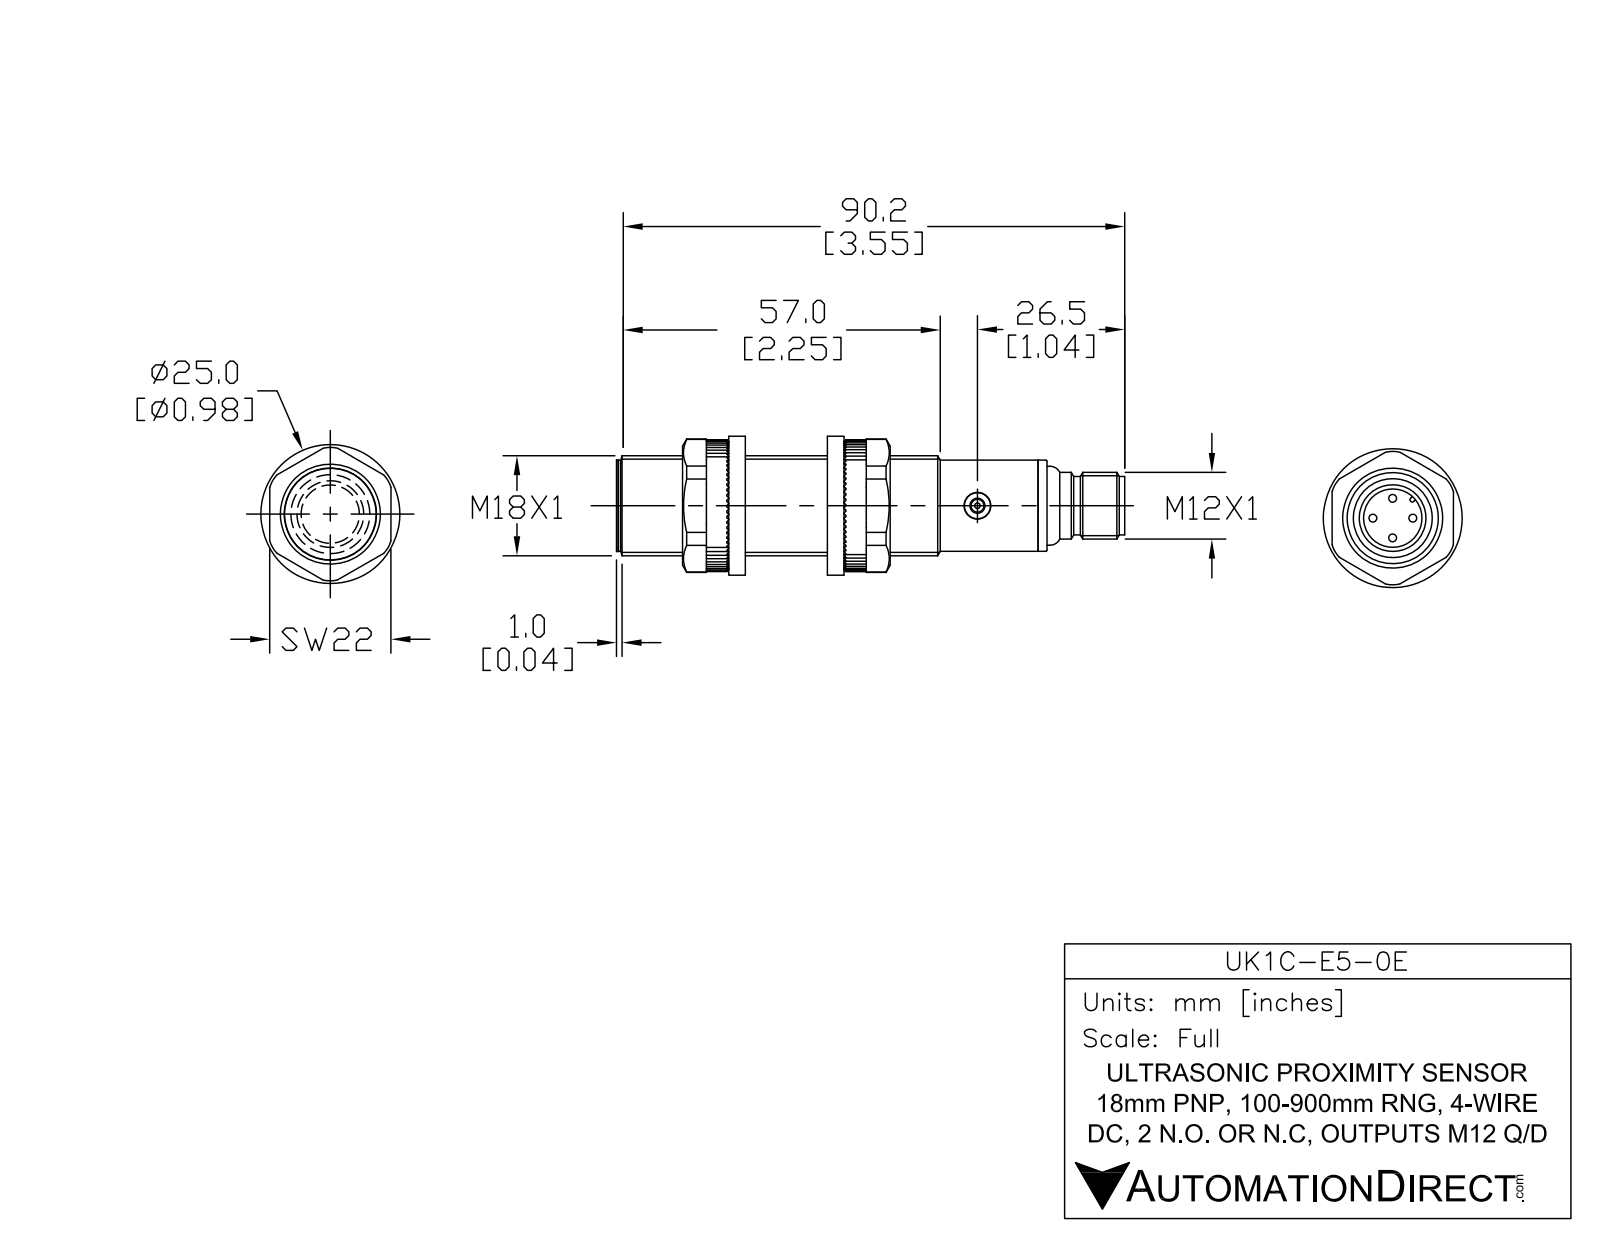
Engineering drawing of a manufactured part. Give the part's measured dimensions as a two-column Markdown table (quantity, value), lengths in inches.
| quantity | value |
| --- | --- |
| part name | UK1C-E5-0E |
| STEP written by | SolidWorks 2017 (AUTOMOTIVE_DESIGN) |
| units | inches |
| bodies | 6 solids, 106 faces (21 planar, 48 cylindrical, 37 other) |
| overall size | 3.606 × 0.709 × 0.709 |
| volume | 1.202 in³ |
| surface area | 10.68 in² |
| round holes (diameter × count) | 0.106 × 1, 0.185 × 1, 0.276 × 1, 0.327 × 1, 0.374 × 1 |
| round bosses / shafts (diameter × count) | 0.039 × 4, 0.709 × 1, 0.654 × 1, 0.646 × 1, 0.622 × 1, 0.559 × 1, 0.472 × 1, 0.413 × 1 |
| partial cylindrical surfaces (radius × count) | 0.024 × 1 |
| main face-to-face distances | 2.957, 0.039, 2.996, 0.037, 2.994, 0.043, 0.157, 3.055, 3.053, 3.016 |
